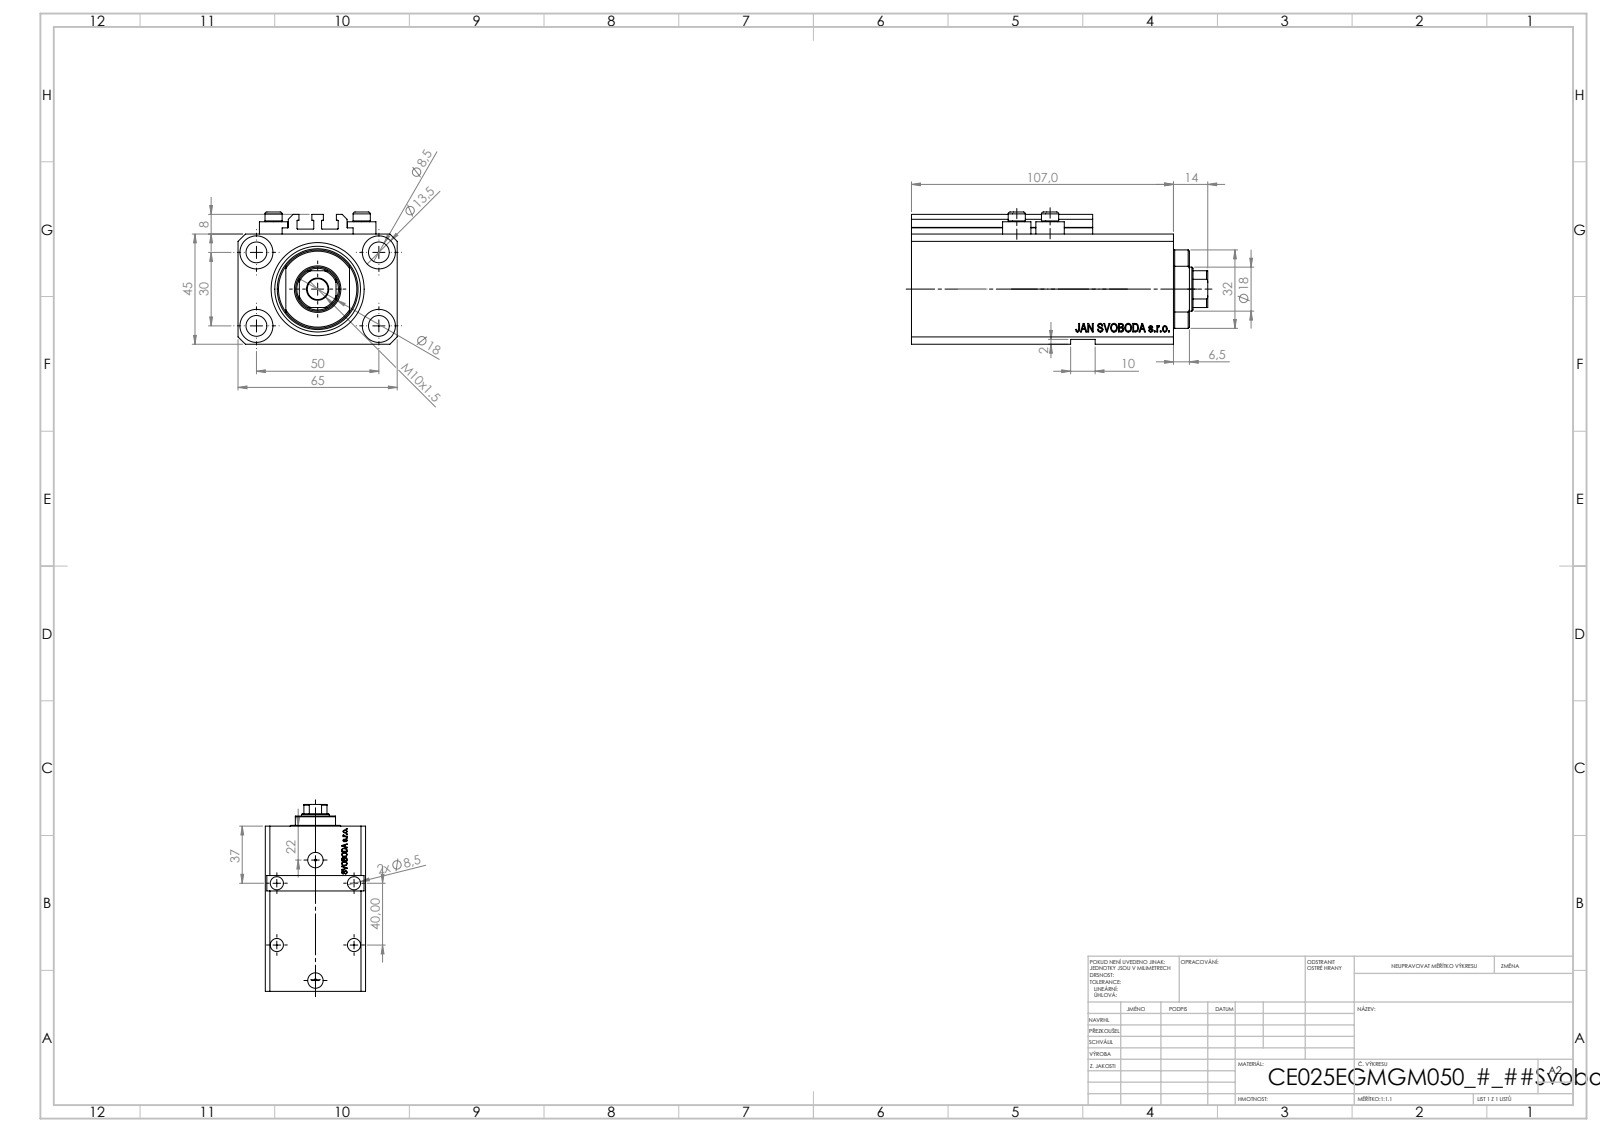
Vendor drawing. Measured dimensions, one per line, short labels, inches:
name: V250CE_E_Body; ALLEN BOLT V250CE; V250CE_C_VCP; V250CE_VC_E
written by: SolidWorks 2019 (CONFIG_CONTROL_DESIGN)
unit: in
bodies: 8 solids, 1087 faces (511 planar, 146 cylindrical, 430 other)
size: 4.764 × 2.559 × 2.126
volume: 16.68 in³; area: 119.2 in²
holes: 9× ⌀0.335, 4× ⌀0.049, 4× ⌀0.157, 4× ⌀0.531, 2× ⌀0.394, 2× ⌀0.518, 2× ⌀0.787, 1× ⌀0.709, 1× ⌀0.984, 1× ⌀1.496
bosses: 4× ⌀0.457, 4× ⌀0.276
rounds: 10× R0.008, 1× R0.335, 1× R0.63
face distances: 1.772, 2.559, 3.661, 0.079, 0.551, 1.85, 4.213, 0.098, 0.394, 0.807
hole spacings: 1.148, 1.969, 0.535, 0.581, 0.595, 1.083, 1.098, 1.181
